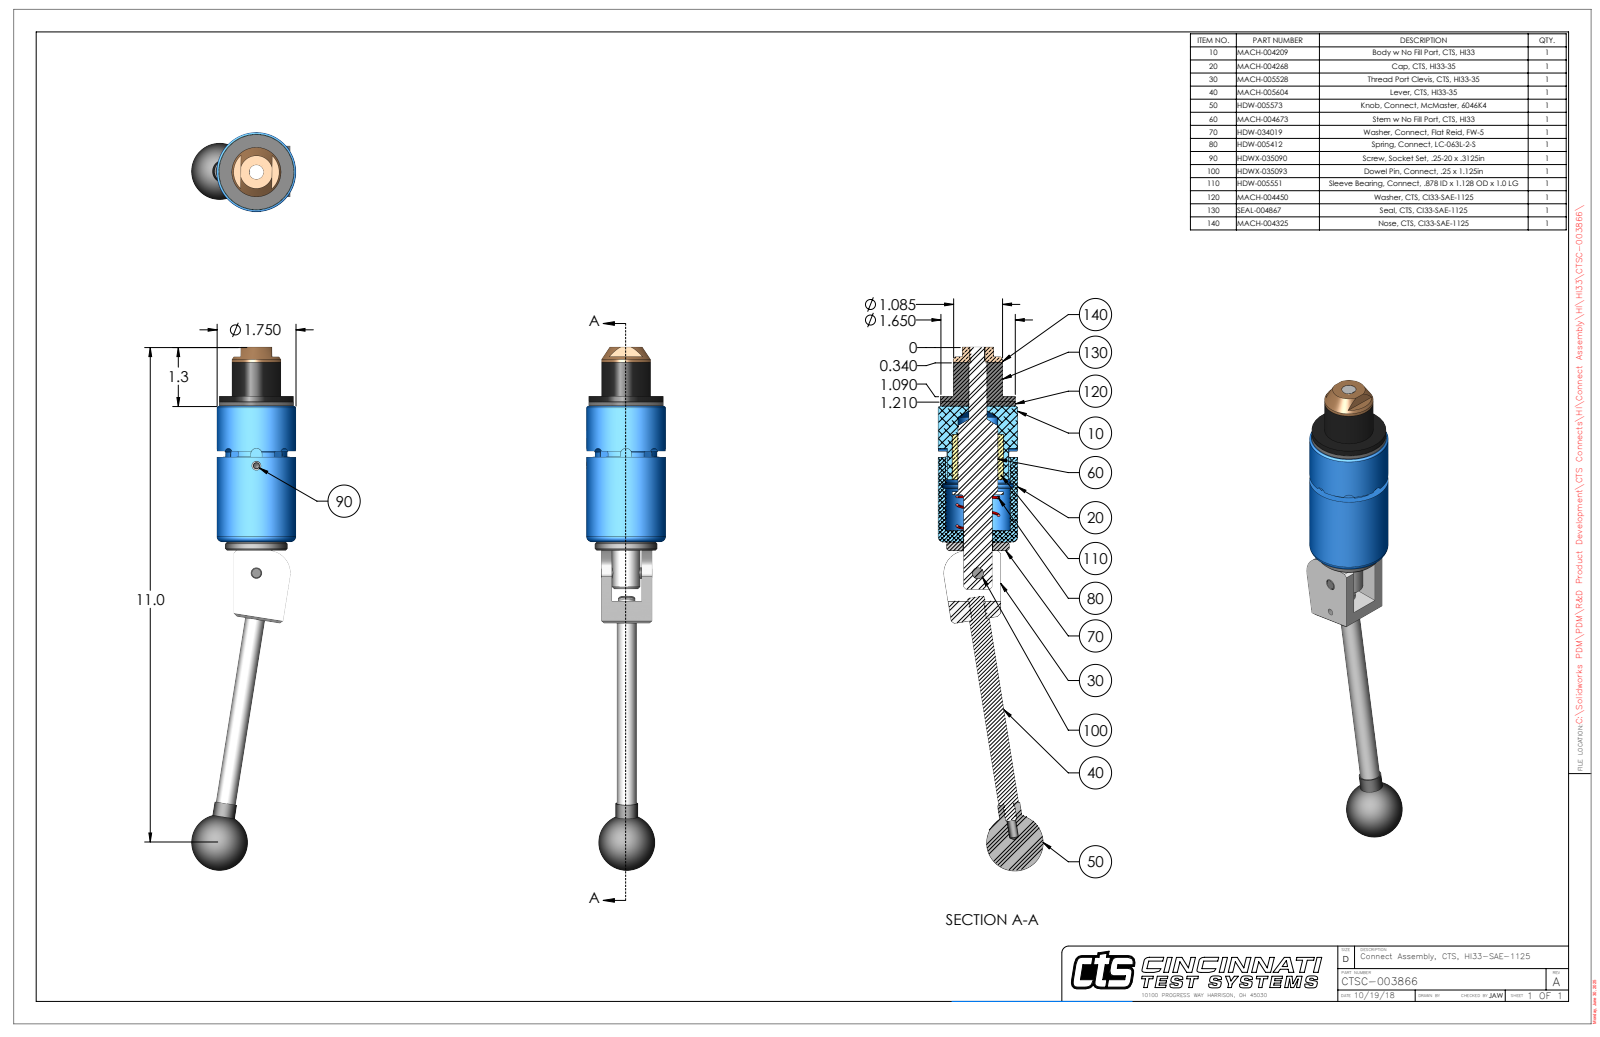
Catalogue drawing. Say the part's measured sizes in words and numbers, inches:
The part is named "CTSC-003866". Its 3-D file was written by "SolidWorks 2023 (AUTOMOTIVE_DESIGN)". It is 9 solids with 265 faces: 101 planar, 105 cylindrical and 59 other. Overall it measures 11.591 by 2.312 by 1.75 inches. Its volume is 11.83 cubic inches and its surface area 71.09 square inches. Round holes: 2 of diameter 0.201, 2 of diameter 0.313, 1 of diameter 0.15, 1 of diameter 0.249, 1 of diameter 0.251, 1 of diameter 0.39, 1 of diameter 0.397, 1 of diameter 0.403, 1 of diameter 0.635, 1 of diameter 0.656. Round bosses or shafts: 2 of diameter 0.312, 2 of diameter 0.25, 1 of diameter 1.75, 1 of diameter 1.65, 1 of diameter 1.38, 1 of diameter 1.085, 1 of diameter 1.085, 1 of diameter 0.625. Partial cylindrical surfaces (rounded edges, fillets, slot ends): 4 of radius 0.125, 2 of radius 0.029, 1 of radius 0.5, 1 of radius 0.695, 1 of radius 0.709, 1 of radius 0.744, 1 of radius 0.808. The main face-to-face distances are 0.098, 3.106, 3.008, 0.87, 0.968, 3.976, 1.12, 3.196, 4.164, 3.294. The hole center spacings are 0.74, 2.376, 3.116.
